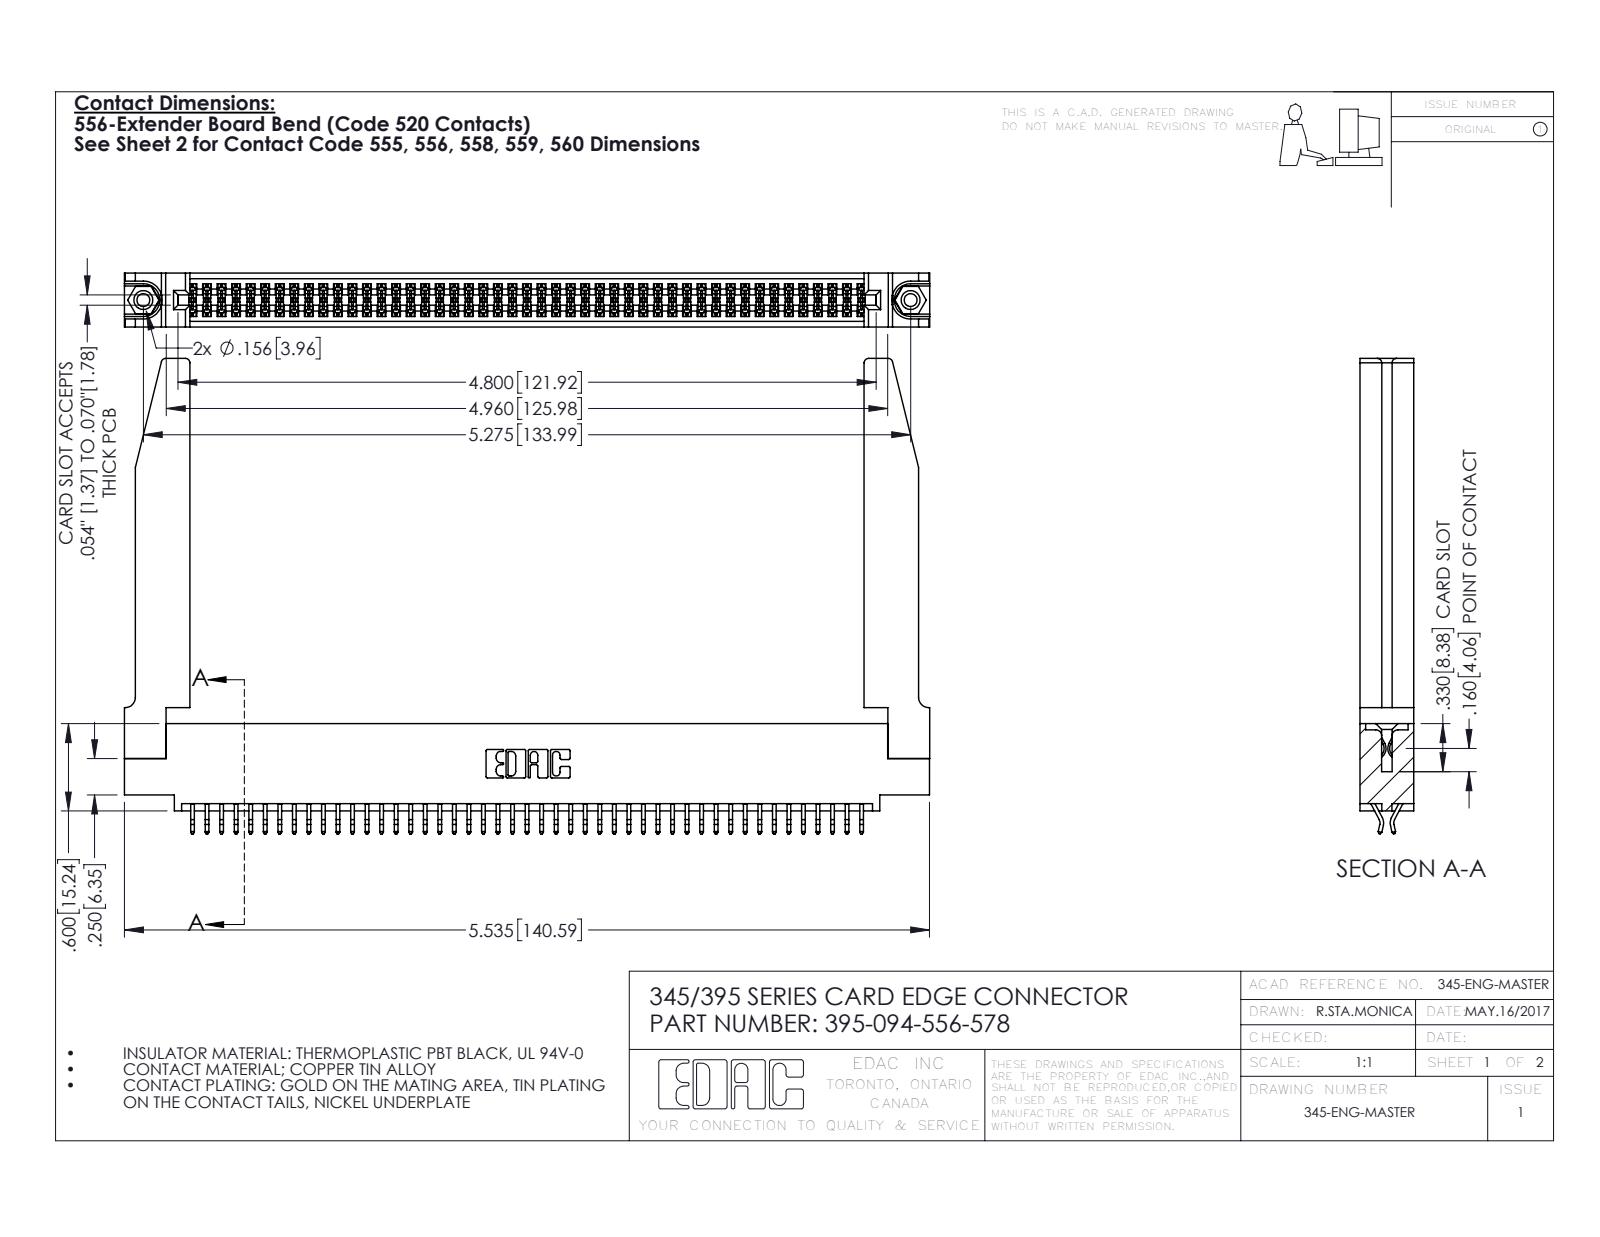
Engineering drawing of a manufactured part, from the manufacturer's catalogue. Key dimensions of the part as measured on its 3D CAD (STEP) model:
Part name (STEP PRODUCT): 345 Part_0.110 Offset - 0.156 Dia-TH; 345-292-001_556 Tail; 345-220-078_345-220-078; 345-250-001_345-250-001-102 (+1 more)
STEP written by: SolidWorks 2016 (CONFIG_CONTROL_DESIGN)
Units: inches
Bodies: 99 solids, 5628 faces (3704 planar, 1872 cylindrical, 52 other)
Overall size (bounding box): 5.536 × 3.267 × 0.37
Volume: 1.306 in³ · Surface area: 41.99 in²
Round holes (diameter × count): ⌀0.089 ×2, ⌀0.125 ×2, ⌀0.156 ×2, ⌀0.064 ×1
Round bosses / shafts (diameter × count): ⌀0.155 ×2
Partial cylindrical surfaces — rounded edges, fillets, slot ends (radius × count): R0.006 ×141, R0.01 ×22, R0.03 ×8, R0.007 ×6, R0.031 ×6, R0.026 ×3, R0.01 ×2, R0.014 ×2
Main face-to-face distances: 0.37, 0.072, 0.298, 0.025, 0.098, 0.272, 0.2, 0.225, 0.148, 0.15
Hole centre spacings: 0.27, 5.039, 5.275
